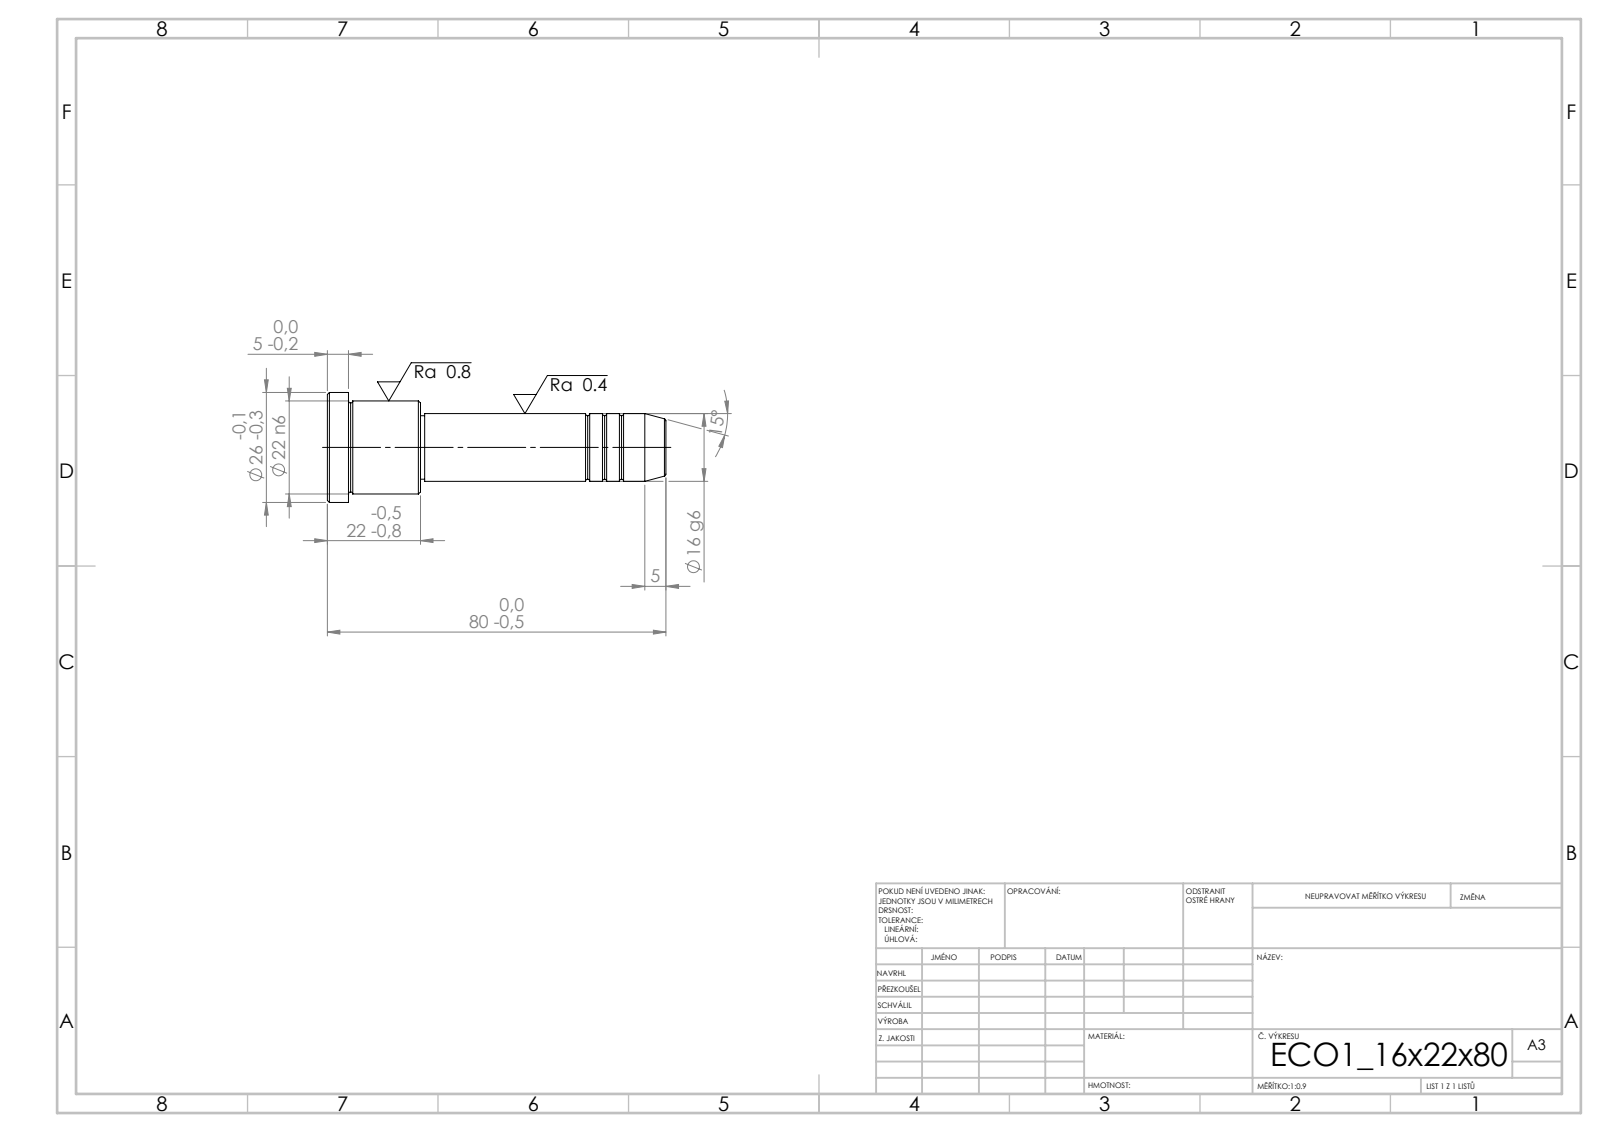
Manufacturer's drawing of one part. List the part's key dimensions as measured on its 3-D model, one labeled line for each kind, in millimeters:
STEP written by: SolidWorks 2019 (CONFIG_CONTROL_DESIGN)
Units: millimetres
Bodies: 1 solid, 43 faces (5 planar, 14 cylindrical, 24 other)
Overall size (bounding box): 80 × 26 × 26
Volume: 20 491 mm³ · Surface area: 5 595 mm²
Round bosses / shafts (diameter × count): ⌀26 ×1, ⌀22 ×1, ⌀16 ×1, ⌀15 ×1
Main face-to-face distances: 22, 17, 5, 58, 75, 80, 57, 1, 18, 23
